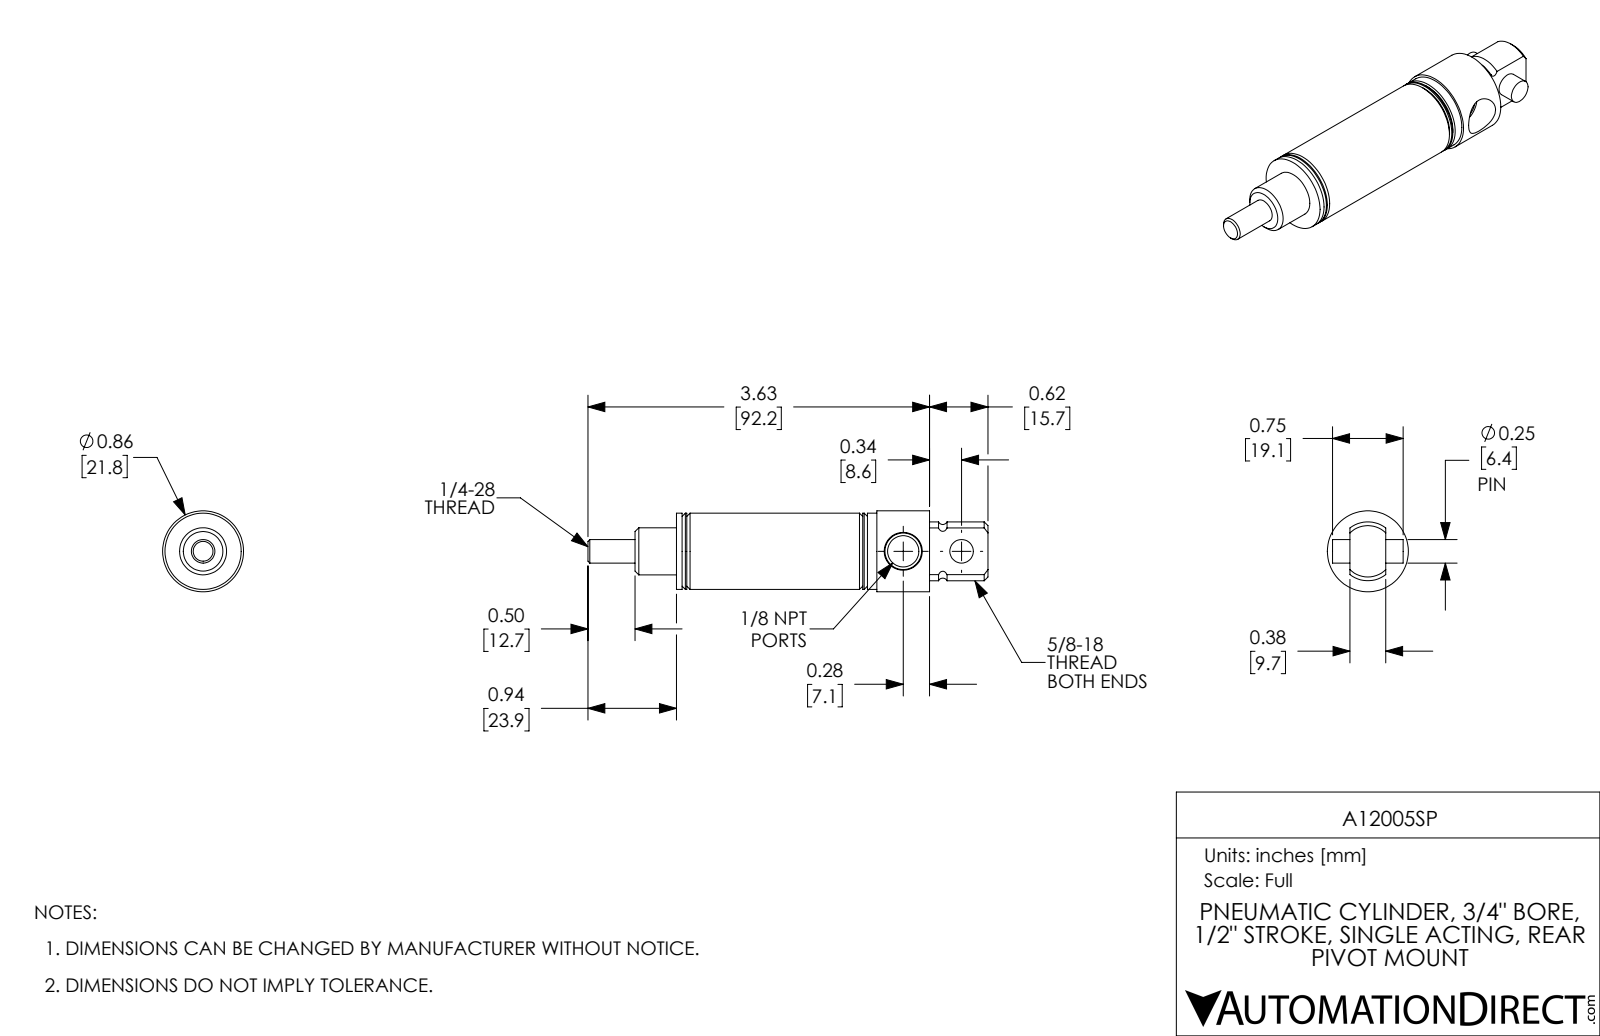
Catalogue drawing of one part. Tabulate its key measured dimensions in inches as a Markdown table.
| quantity | value |
| --- | --- |
| part name | A12005SP; A12005SP-Pin; A12005SP-Rod; A12005SP-MainBody |
| STEP written by | SolidWorks 2017 (AUTOMOTIVE_DESIGN) |
| units | inches |
| bodies | 3 solids, 73 faces (19 planar, 32 cylindrical, 22 other) |
| overall size | 4.25 × 0.86 × 0.86 |
| volume | 1.433 in³ |
| surface area | 19.71 in² |
| round holes (diameter × count) | 0.25 × 2, 0.332 × 1, 0.75 × 1 |
| round bosses / shafts (diameter × count) | 0.86 × 1, 0.81 × 1, 0.5 × 1 |
| partial cylindrical surfaces (radius × count) | 0.313 × 1 |
| main face-to-face distances | 0.5, 0.845, 1.345, 1.845, 1, 2.69, 0.38, 1.285, 1.785, 0.62 |
| hole center spacings | 0.62 |
